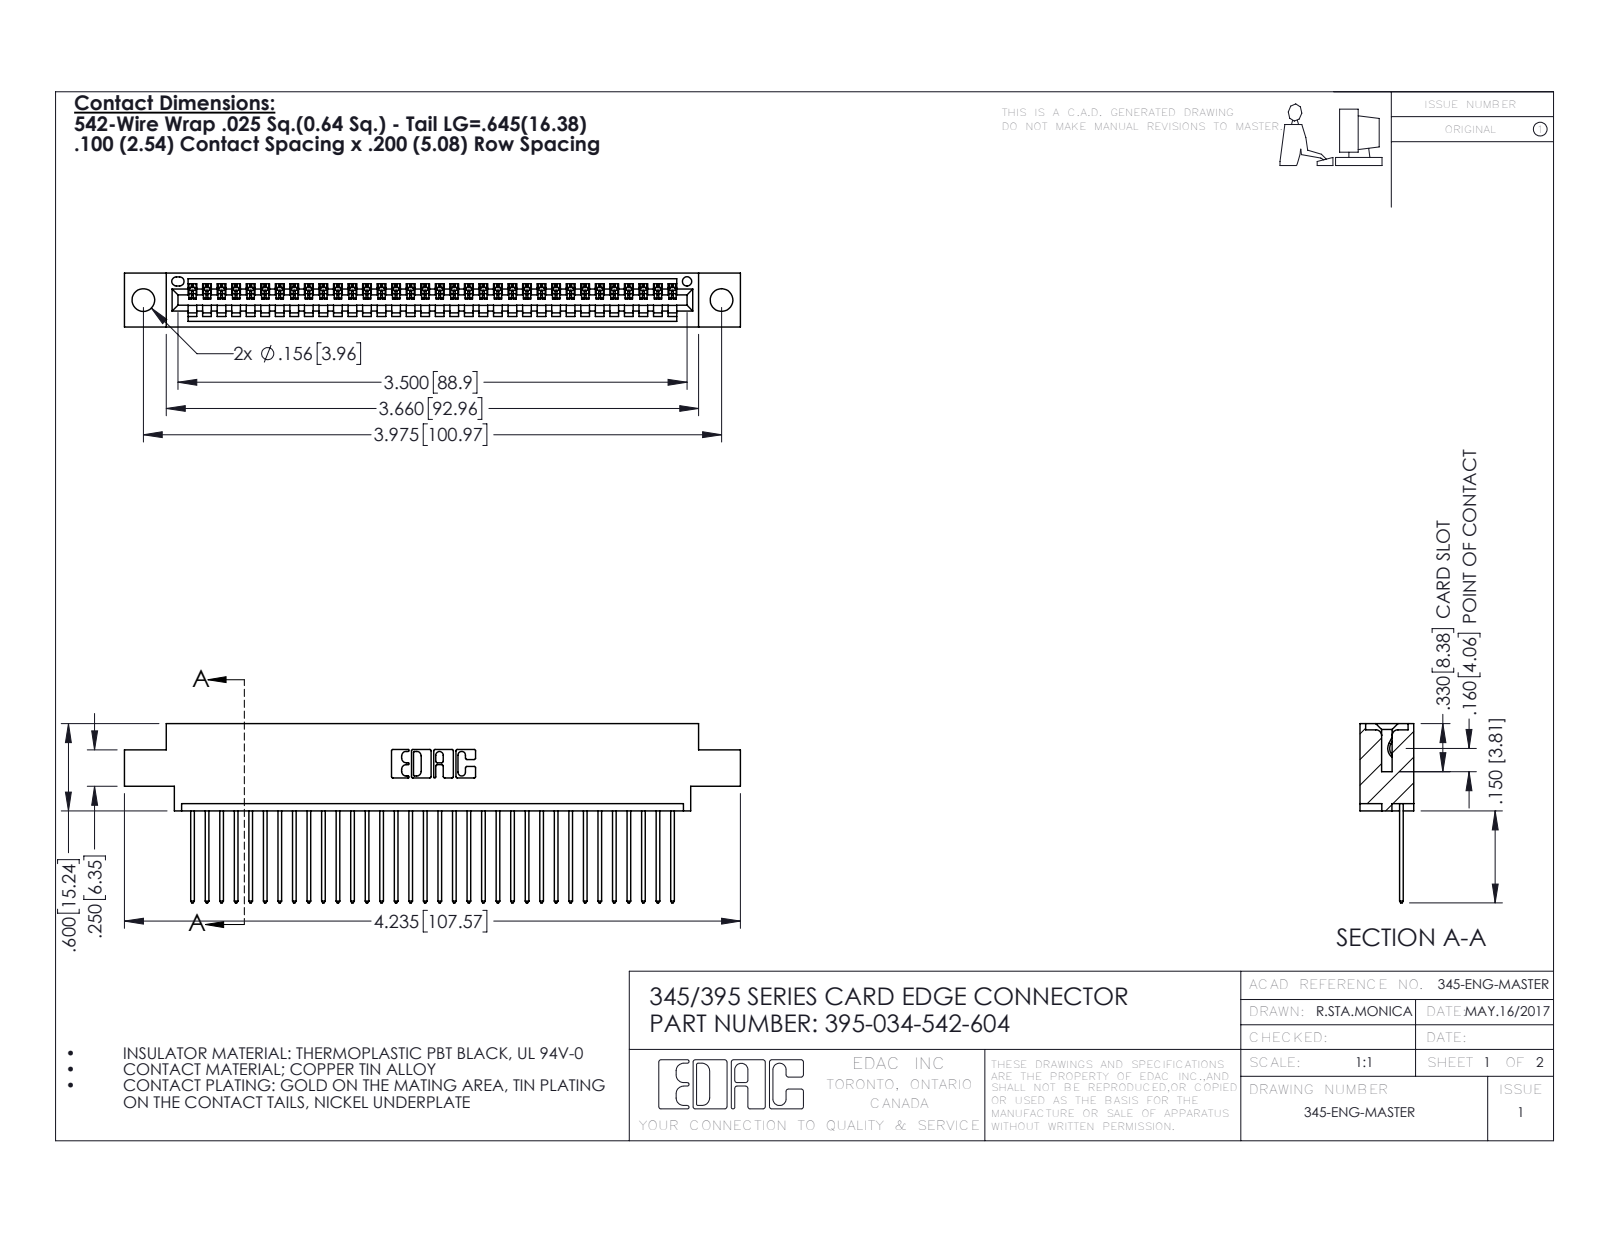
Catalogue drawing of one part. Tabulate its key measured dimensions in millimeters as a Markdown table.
| quantity | value |
| --- | --- |
| part name | 345-292-001_345-293-142; 345 Part_0.170 Offset - 0.156 Dia-TH; 395-034-542-604 |
| STEP written by | SolidWorks 2016 (CONFIG_CONTROL_DESIGN) |
| units | millimeters |
| bodies | 35 solids, 2102 faces (1444 planar, 658 cylindrical, 0 other) |
| overall size | 107.6 × 31.3 × 9.4 |
| volume | 10 000 mm³ |
| surface area | 13 630 mm² |
| round holes (diameter × count) | 4 × 2, 1.6 × 1 |
| partial cylindrical surfaces (radius × count) | 0.2 × 68, 0.3 × 68, 0.3 × 22, 0.2 × 6, 0.8 × 6, 0.7 × 3, 0.8 × 2, 1 × 2 |
| main face-to-face distances | 7.6, 1.8, 9.4, 2.5, 6.9, 0.6, 5.1, 5.7, 4.4, 3.8 |
| hole center spacings | 6.9, 95, 101 |
